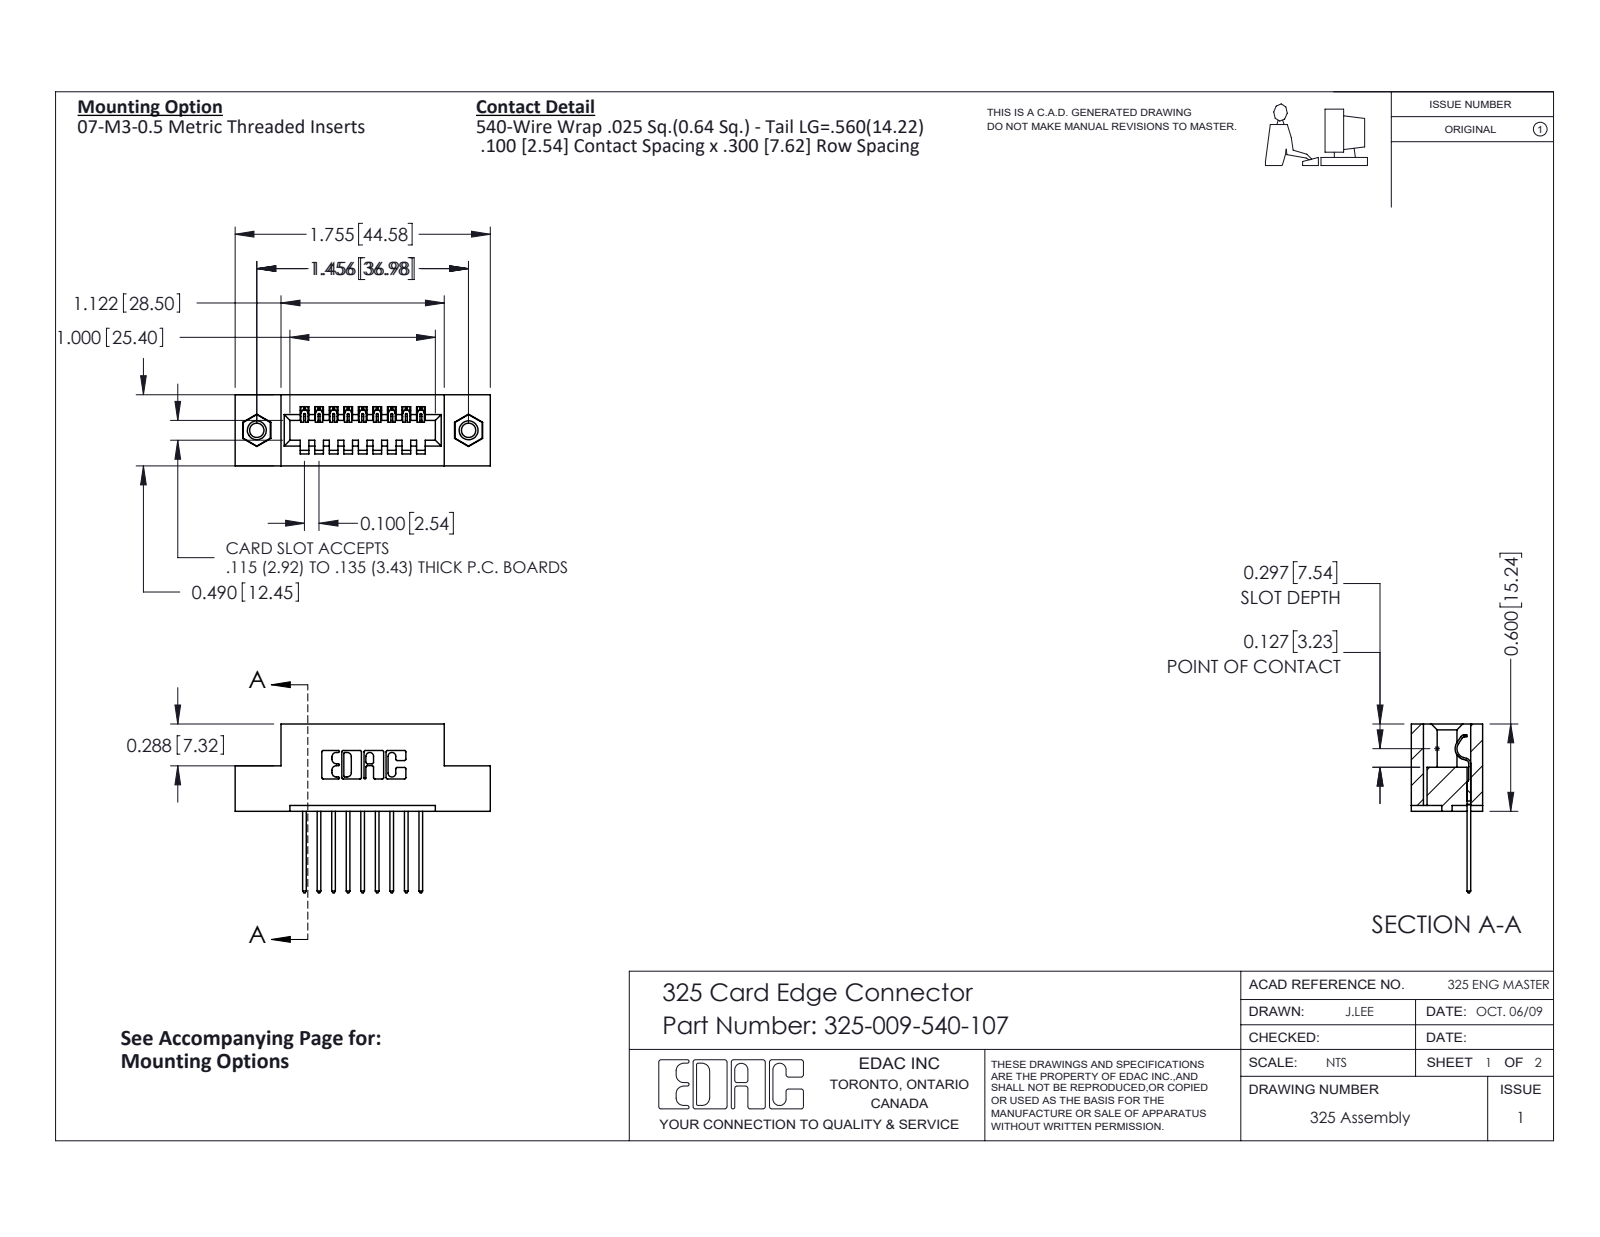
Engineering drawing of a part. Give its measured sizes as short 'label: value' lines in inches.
name: 325-292-001_325-293-140; 325 Part_TI; 325-009-540-107; 345-250-001_345-250-005-103
written by: SolidWorks 2016 (CONFIG_CONTROL_DESIGN)
unit: in
bodies: 12 solids, 696 faces (480 planar, 200 cylindrical, 16 other)
size: 1.755 × 1.16 × 0.49
volume: 0.329 in³; area: 8.455 in²
holes: 2× ⌀0.098, 2× ⌀0.125, 2× ⌀0.16
bosses: 2× ⌀0.155
rounds: 22× R0.01, 18× R0.006, 18× R0.01, 6× R0.007, 6× R0.031, 3× R0.026, 1× R0.014, 1× R0.022
face distances: 0.3, 0.04, 0.083, 0.407, 0.1, 0.49, 0.2, 0.6, 0.4, 0.107
hole spacings: 1.456
